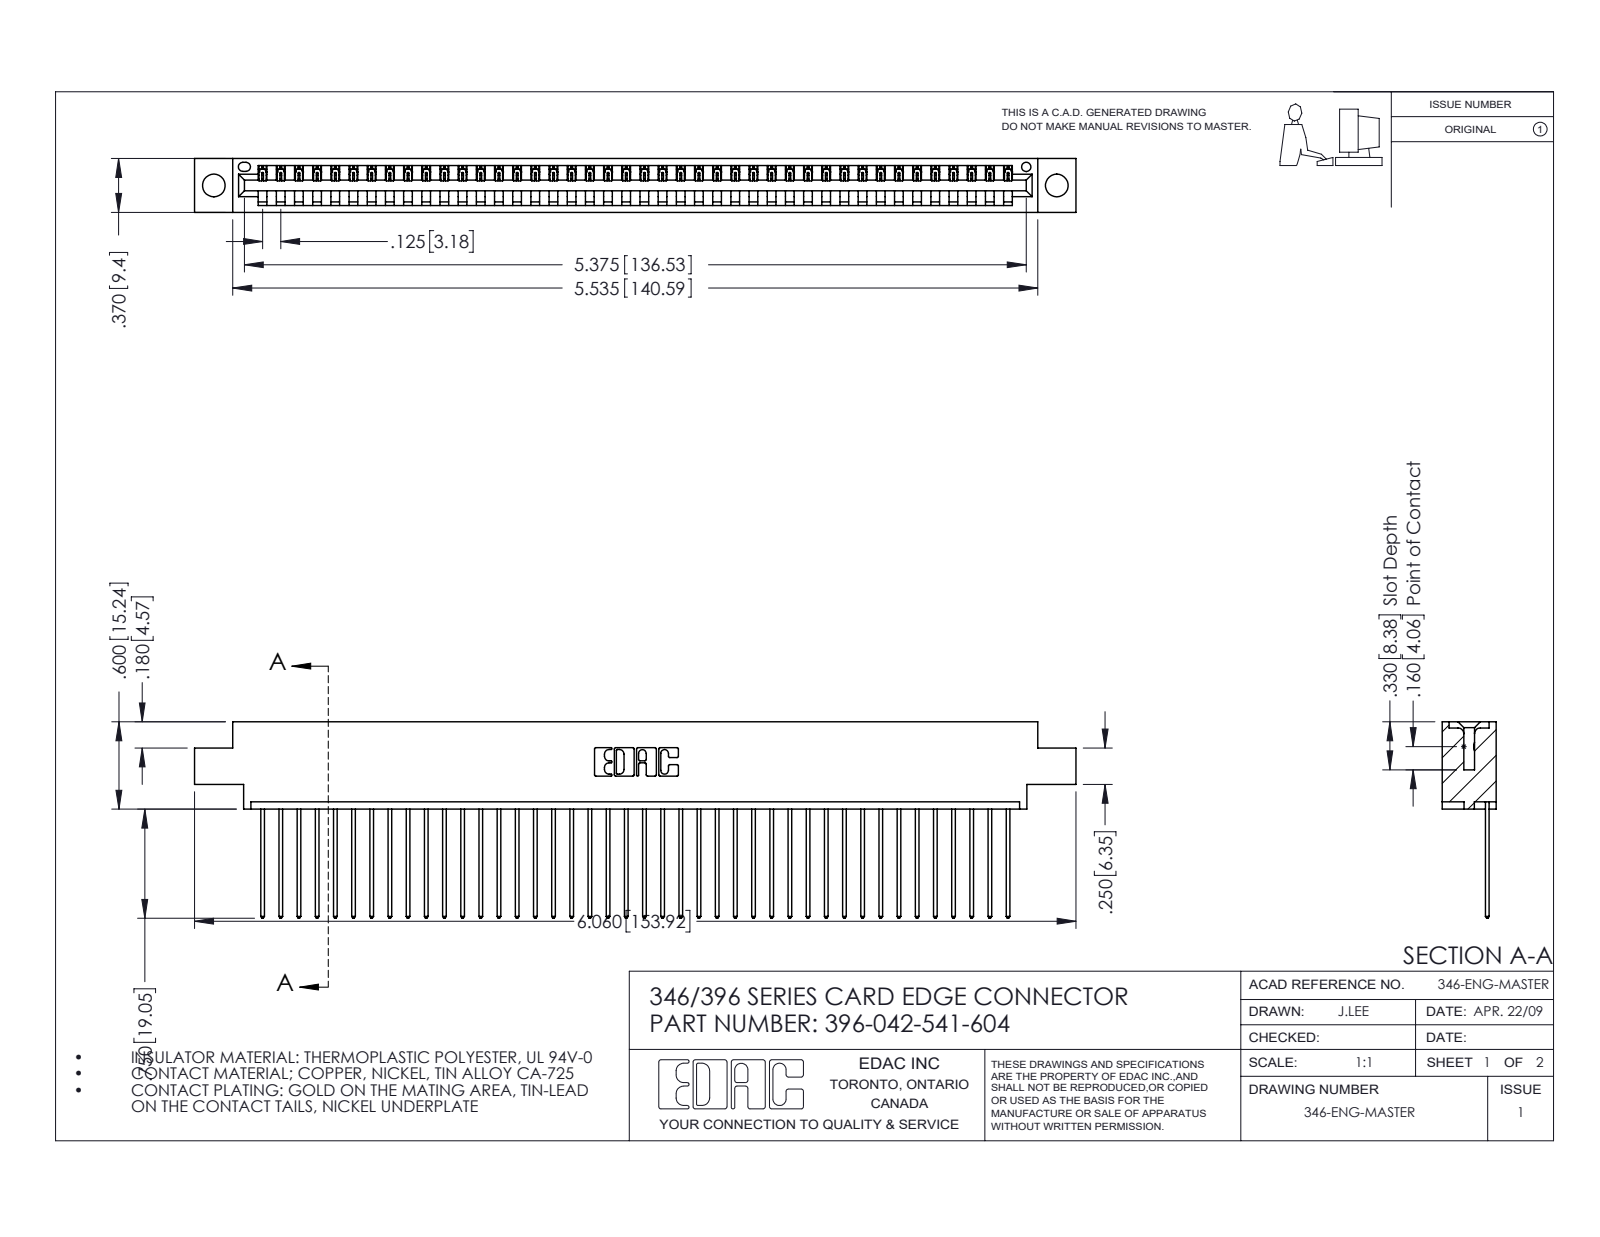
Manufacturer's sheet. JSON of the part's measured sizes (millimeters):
{"part_name": "346 Part_0.170 Offset - 0.156 Dia-TH; 345-292-001_345-293-141; 396-042-541-604", "step_written_by": "SolidWorks 2016 (CONFIG_CONTROL_DESIGN)", "units": "millimeters", "bodies": {"solids": 43, "faces": 2562, "planar": 1760, "cylindrical": 802, "other": 0}, "overall_size": [153.9, 34.3, 9.4], "volume_mm3": 14600, "surface_area_mm2": 19080, "round_holes": [[4, 2], [1.6, 1]], "partial_cylinders_radius": [[0.2, 84], [0.3, 84], [0.3, 22], [0.2, 6], [0.8, 6], [0.7, 3], [0.8, 2], [1, 2]], "face_to_face_distances": [1.2, 8.2, 9.4, 6.4, 1.8, 7.6, 0.6, 3.8, 5.6, 2.5], "hole_center_spacings": [6.2, 141.9, 147.2]}
